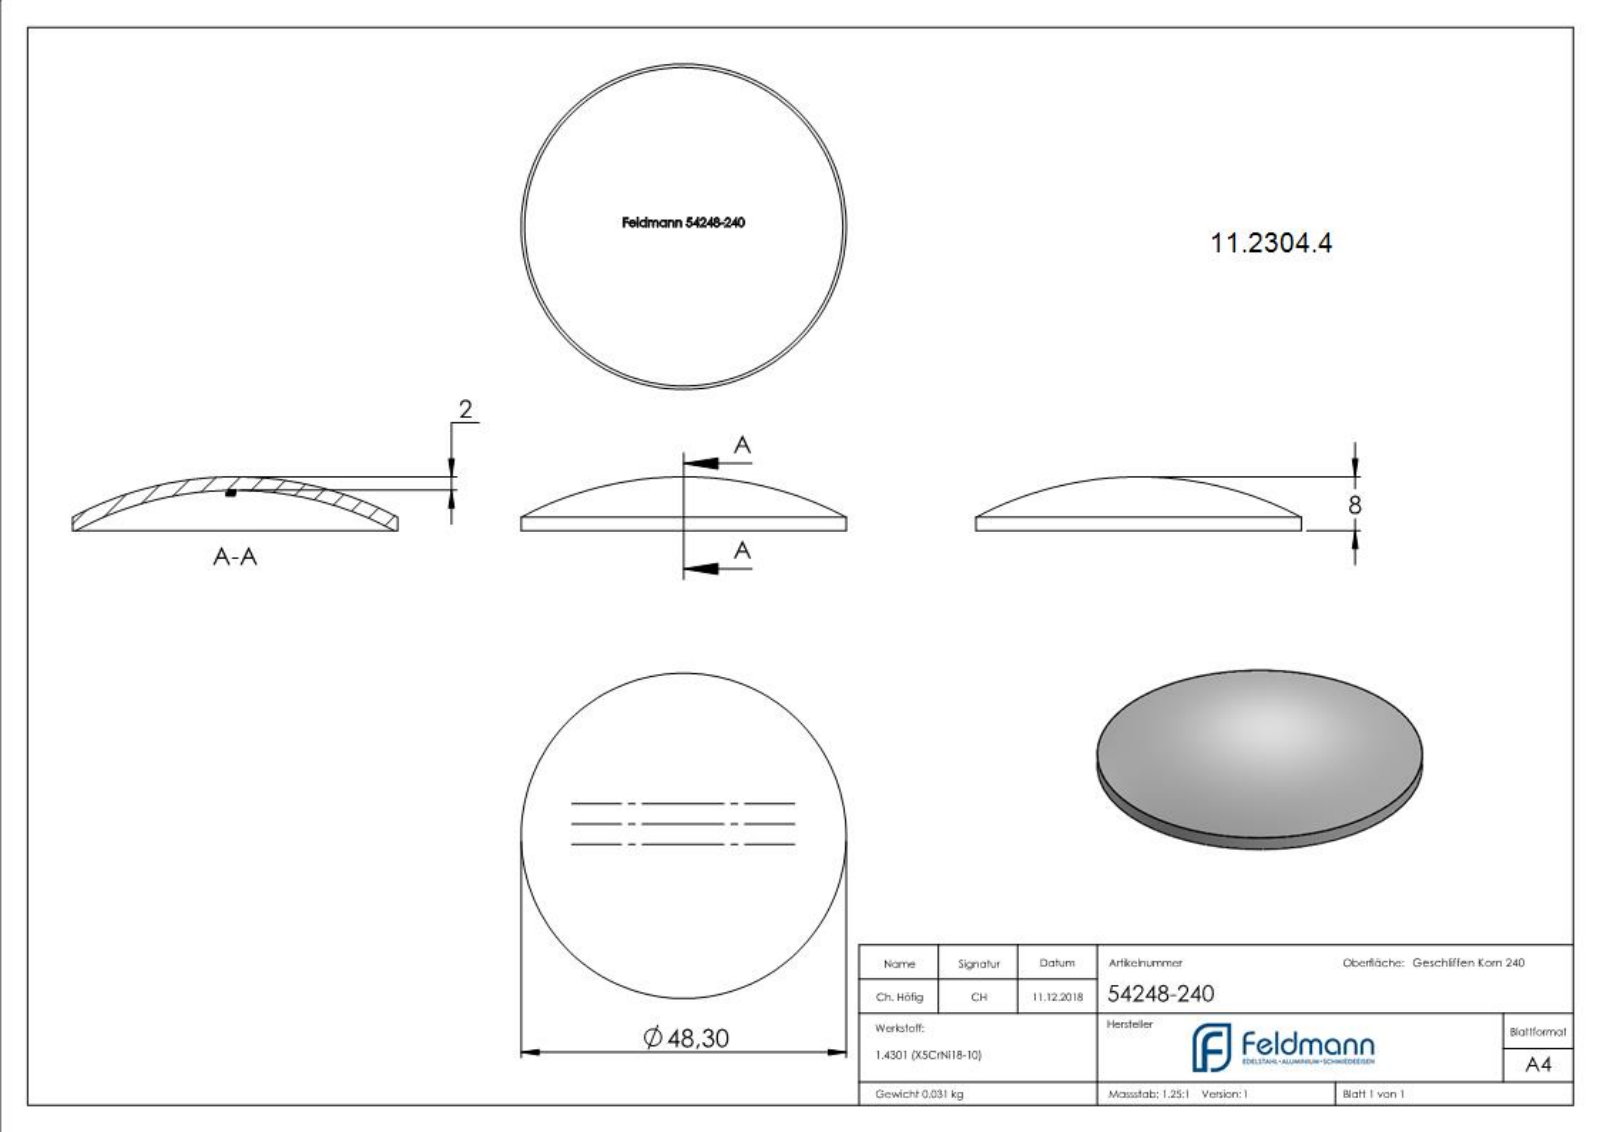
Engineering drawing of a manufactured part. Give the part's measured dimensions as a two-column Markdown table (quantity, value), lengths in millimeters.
| quantity | value |
| --- | --- |
| part name | 54248-240 |
| STEP written by | SolidWorks 2015 (CONFIG_CONTROL_DESIGN) |
| units | millimeters |
| bodies | 1 solid, 254 faces (116 planar, 2 cylindrical, 136 other) |
| overall size | 48.3 × 48.3 × 8 |
| volume | 3 890 mm³ |
| surface area | 4 204 mm² |
| round bosses / shafts (diameter × count) | 48.3 × 1 |
| main face-to-face distances | 0.44, 3.66, 0.39, 12.97, 2.97, 0.31, 4.7, 13.09, 0.88, 14.62 |
